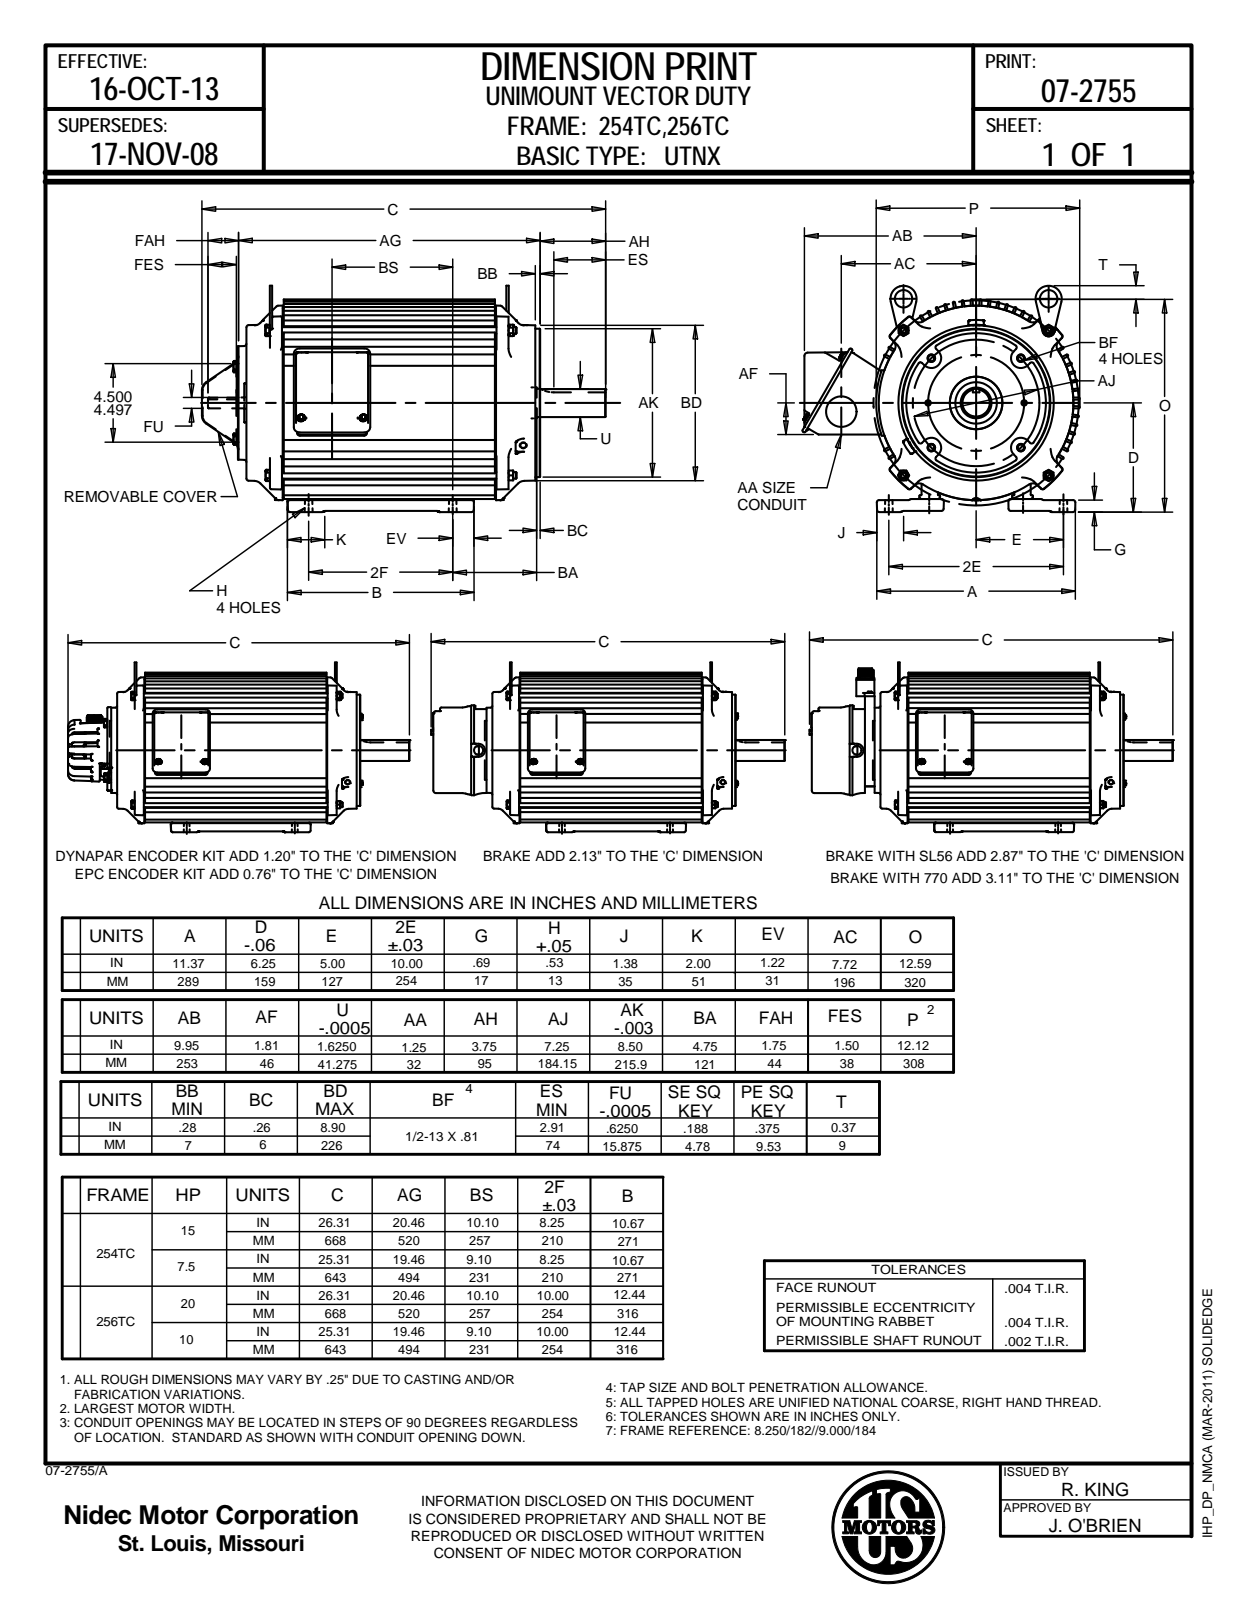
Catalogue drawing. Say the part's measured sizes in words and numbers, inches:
The part is named "UN10T3BC". Its 3-D file was written by "SolidWorks 2021 (AUTOMOTIVE_DESIGN)". It is 4 solids with 2374 faces: 508 planar, 807 cylindrical and 1059 other. Overall it measures 25.407 by 16.249 by 13.101 inches. Its volume is 2 163 cubic inches and its surface area 1 758 square inches. Round holes: 4 of diameter 0.313, 4 of diameter 0.328, 4 of diameter 0.344, 4 of diameter 0.406, 2 of diameter 0.107, 2 of diameter 1, 2 of diameter 1.75, 1 of diameter 1.387. Round bosses or shafts: 1 of diameter 10.847, 1 of diameter 8.5, 1 of diameter 6.5, 1 of diameter 4.5, 1 of diameter 1.77, 1 of diameter 1.625, 1 of diameter 1.375, 1 of diameter 0.625. Partial cylindrical surfaces (rounded edges, fillets, slot ends): 213 of radius 0.063, 59 of radius 0.125, 56 of radius 0.06, 38 of radius 0.031, 24 of radius 0.188, 12 of radius 0.219, 8 of radius 0.18, 6 of radius 0.016. The main face-to-face distances are 0.313, 0.626, 0.125, 18.274, 0.265, 18.539, 0.2, 0.065, 18.339, 2.05. The hole center spacings are 2.937, 6.569, 5.875, 2.317, 3.754, 4.154, 5.186, 6.659.
